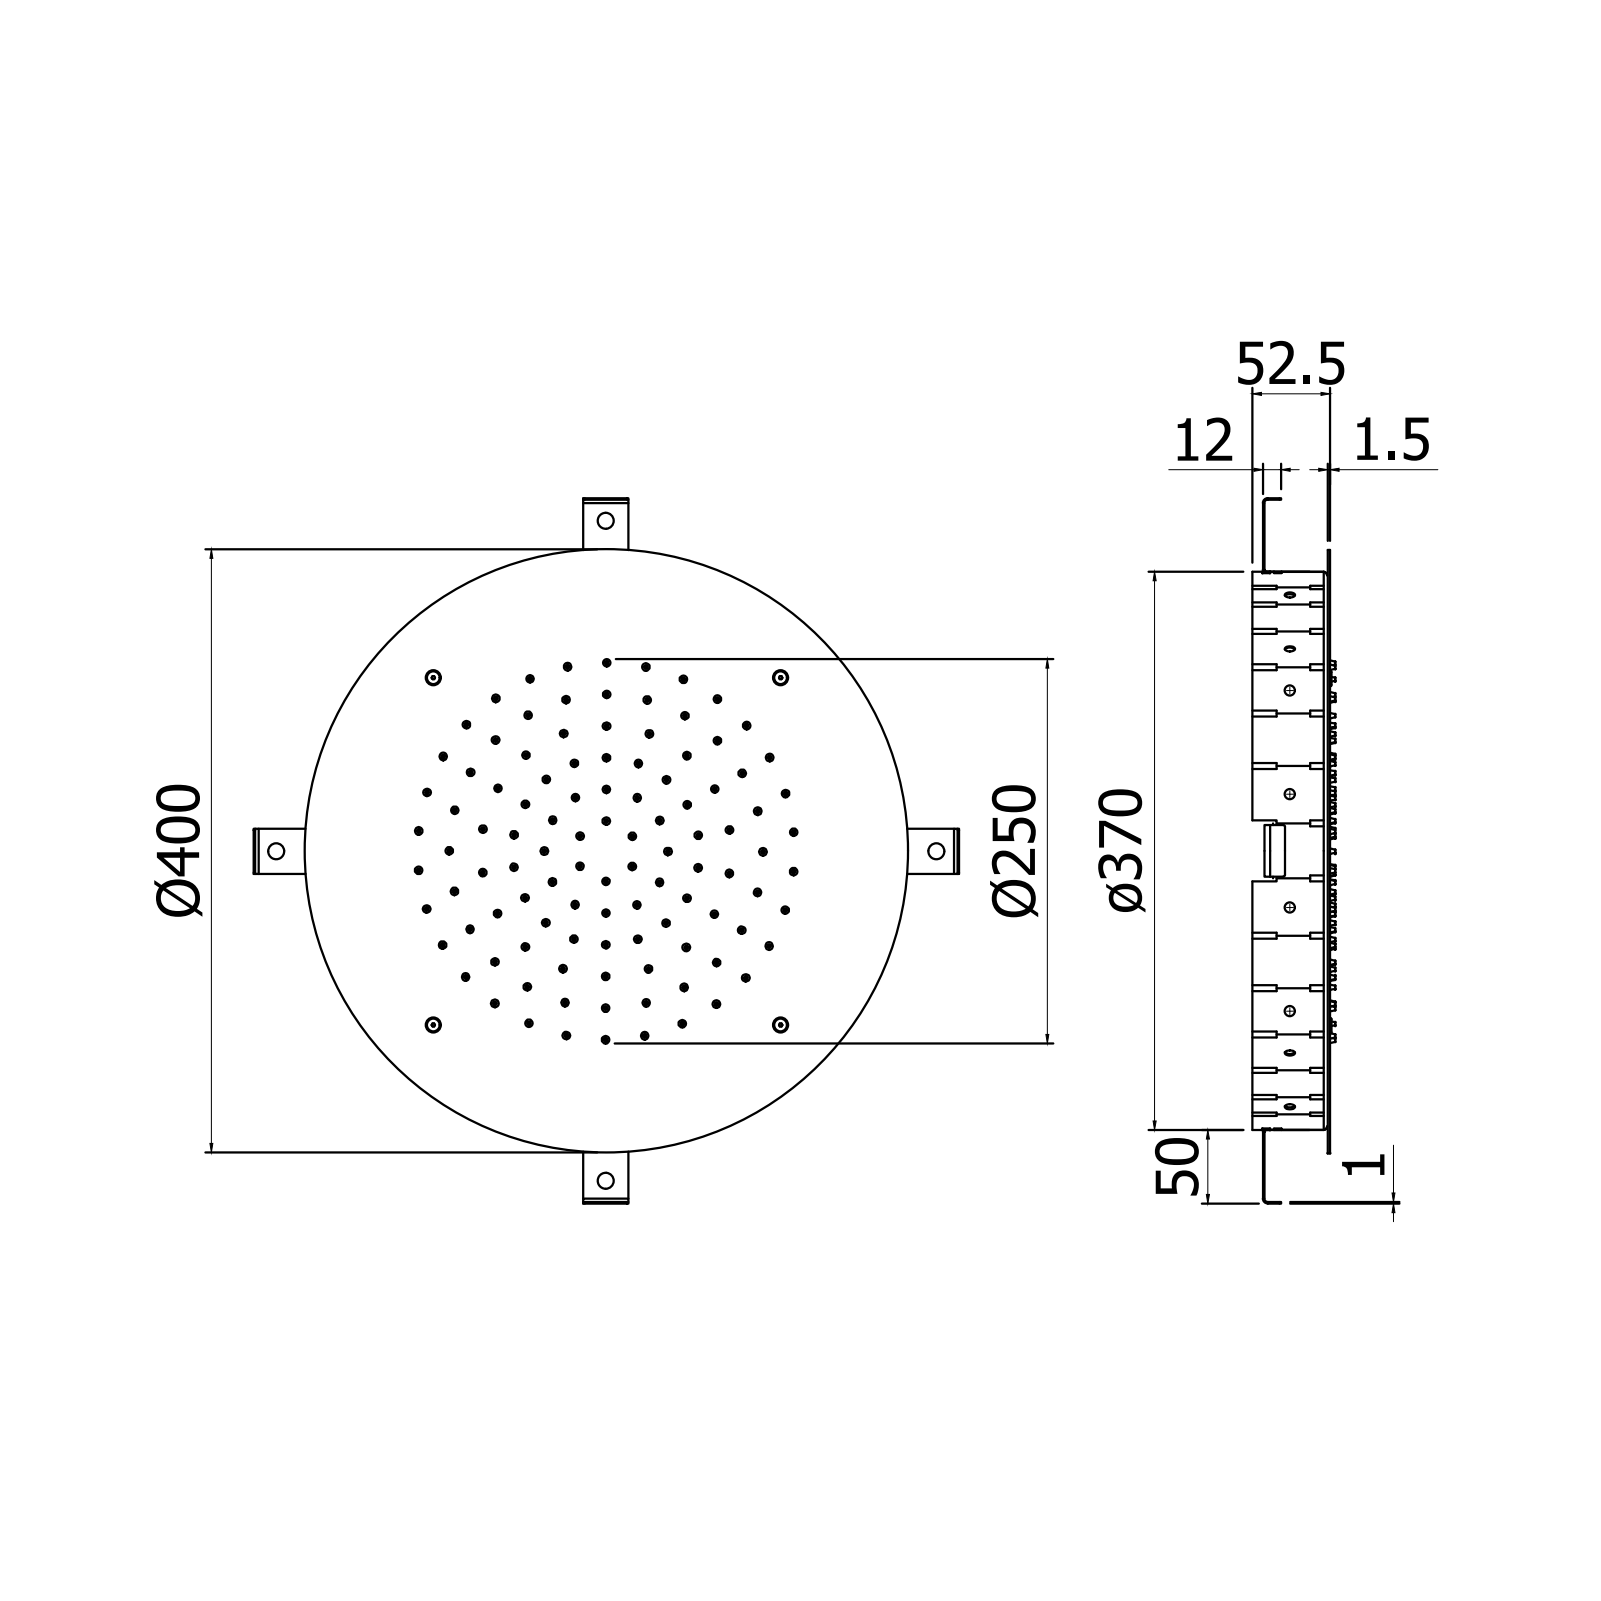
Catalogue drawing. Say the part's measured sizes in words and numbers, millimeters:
The part is named "ZSOF303CR". Its 3-D file was written by "CREO PARAMETRIC BY PTC INC, 2020044 (CONFIG_CONTROL_DESIGN)". It is 1 solid with 1732 faces: 146 planar, 482 cylindrical and 1104 other. Overall it measures 400 by 400 by 4.8 millimeters. Its volume is 189 089 cubic millimeters and its surface area 261 948 square millimeters. Round holes: 108 of diameter 1.5, 108 of diameter 5, 4 of diameter 7. Round bosses or shafts: 4 of diameter 10, 4 of diameter 5, 1 of diameter 400. Partial cylindrical surfaces (rounded edges, fillets, slot ends): 24 of radius 0.2. The main face-to-face distances are 1.5, 1, 2.5, 2.3, 3.3, 4.8, 2, 65.4, 258.48, 2.01. The hole center spacings are 71.88, 109.42, 216.51, 27.15, 42, 65.27, 80.42, 89.12.
